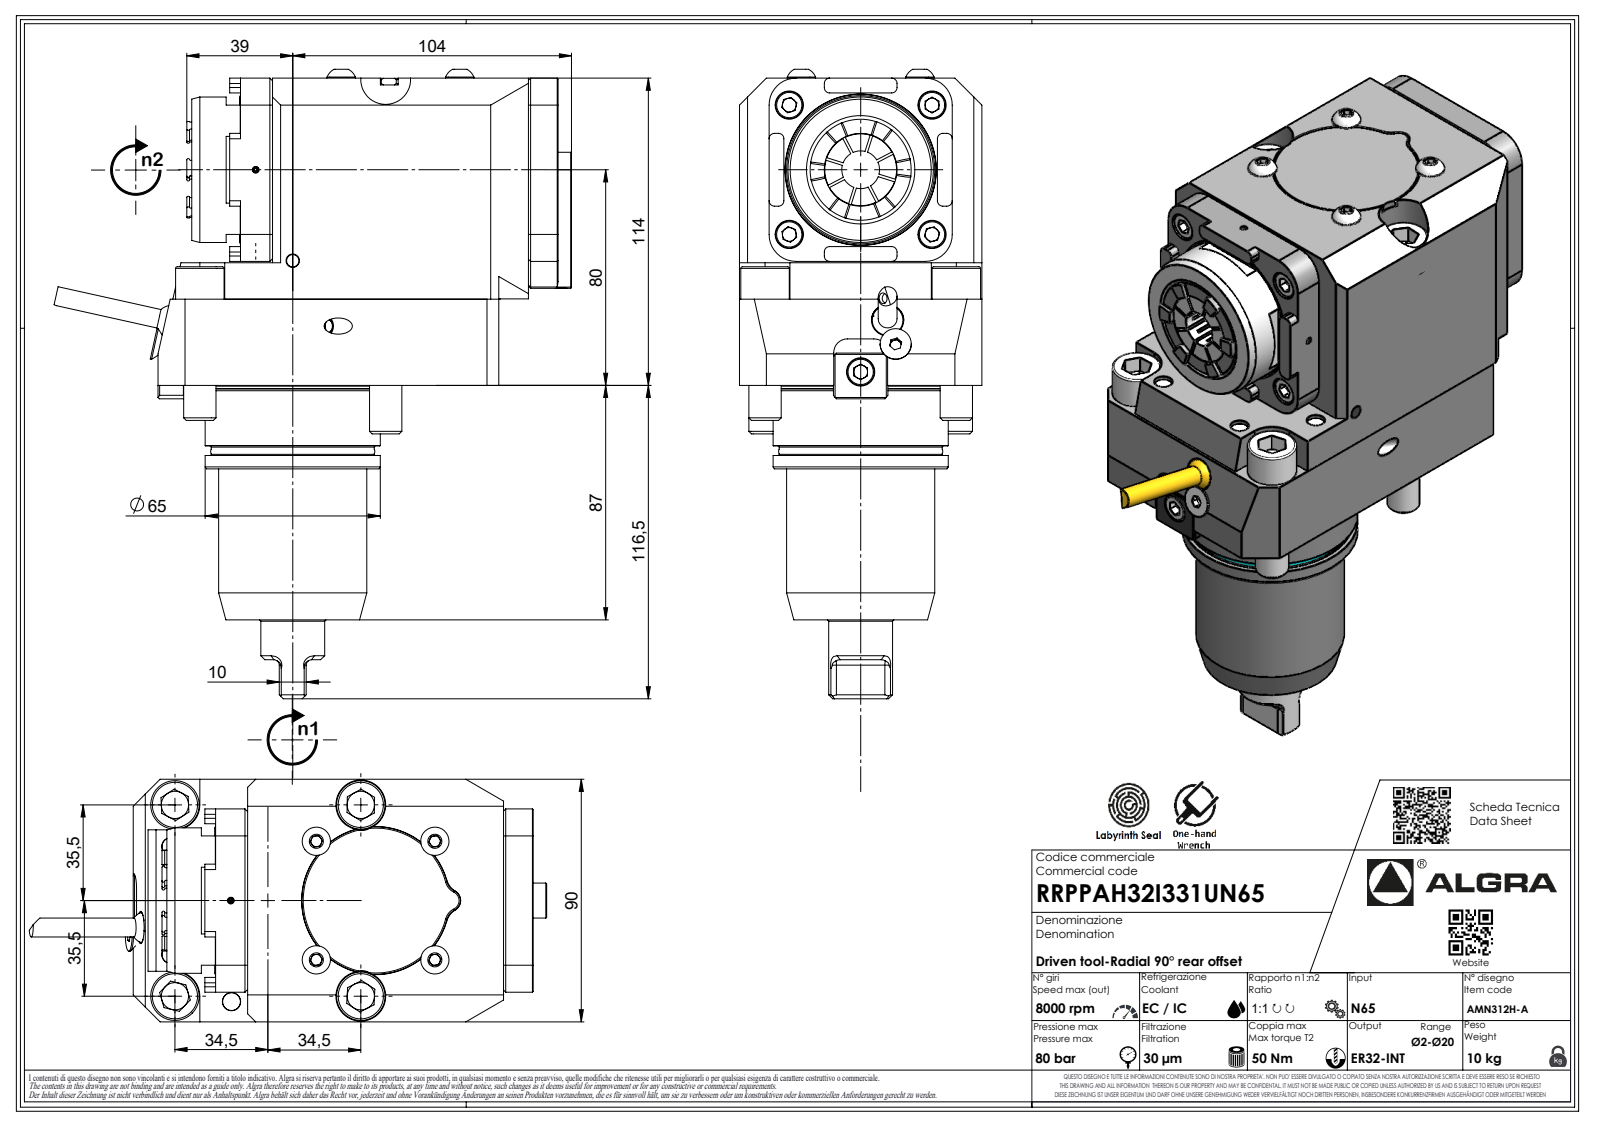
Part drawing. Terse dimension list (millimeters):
name: RRPPAH32I331UN65
written by: SolidWorks 2023 (AUTOMOTIVE_DESIGN)
unit: mm
bodies: 1 solid, 613 faces (366 planar, 97 cylindrical, 150 other)
size: 233.6 × 192.09 × 90
volume: 1 480 000 mm³; area: 103 439 mm²
holes: 1× ⌀2.1, 1× ⌀4, 1× ⌀5, 1× ⌀6, 1× ⌀56.2
bosses: 4× ⌀10.5, 3× ⌀12, 2× ⌀18, 1× ⌀65, 1× ⌀64.6, 1× ⌀60.5, 1× ⌀56, 1× ⌀55
rounds: 23× R2, 7× R0.33, 7× R0.52, 7× R3.7, 6× R10, 4× R9.25, 1× R0.21, 1× R2.5
face distances: 114, 90, 11, 68.5, 22, 45.5, 79, 68, 136, 11.9
